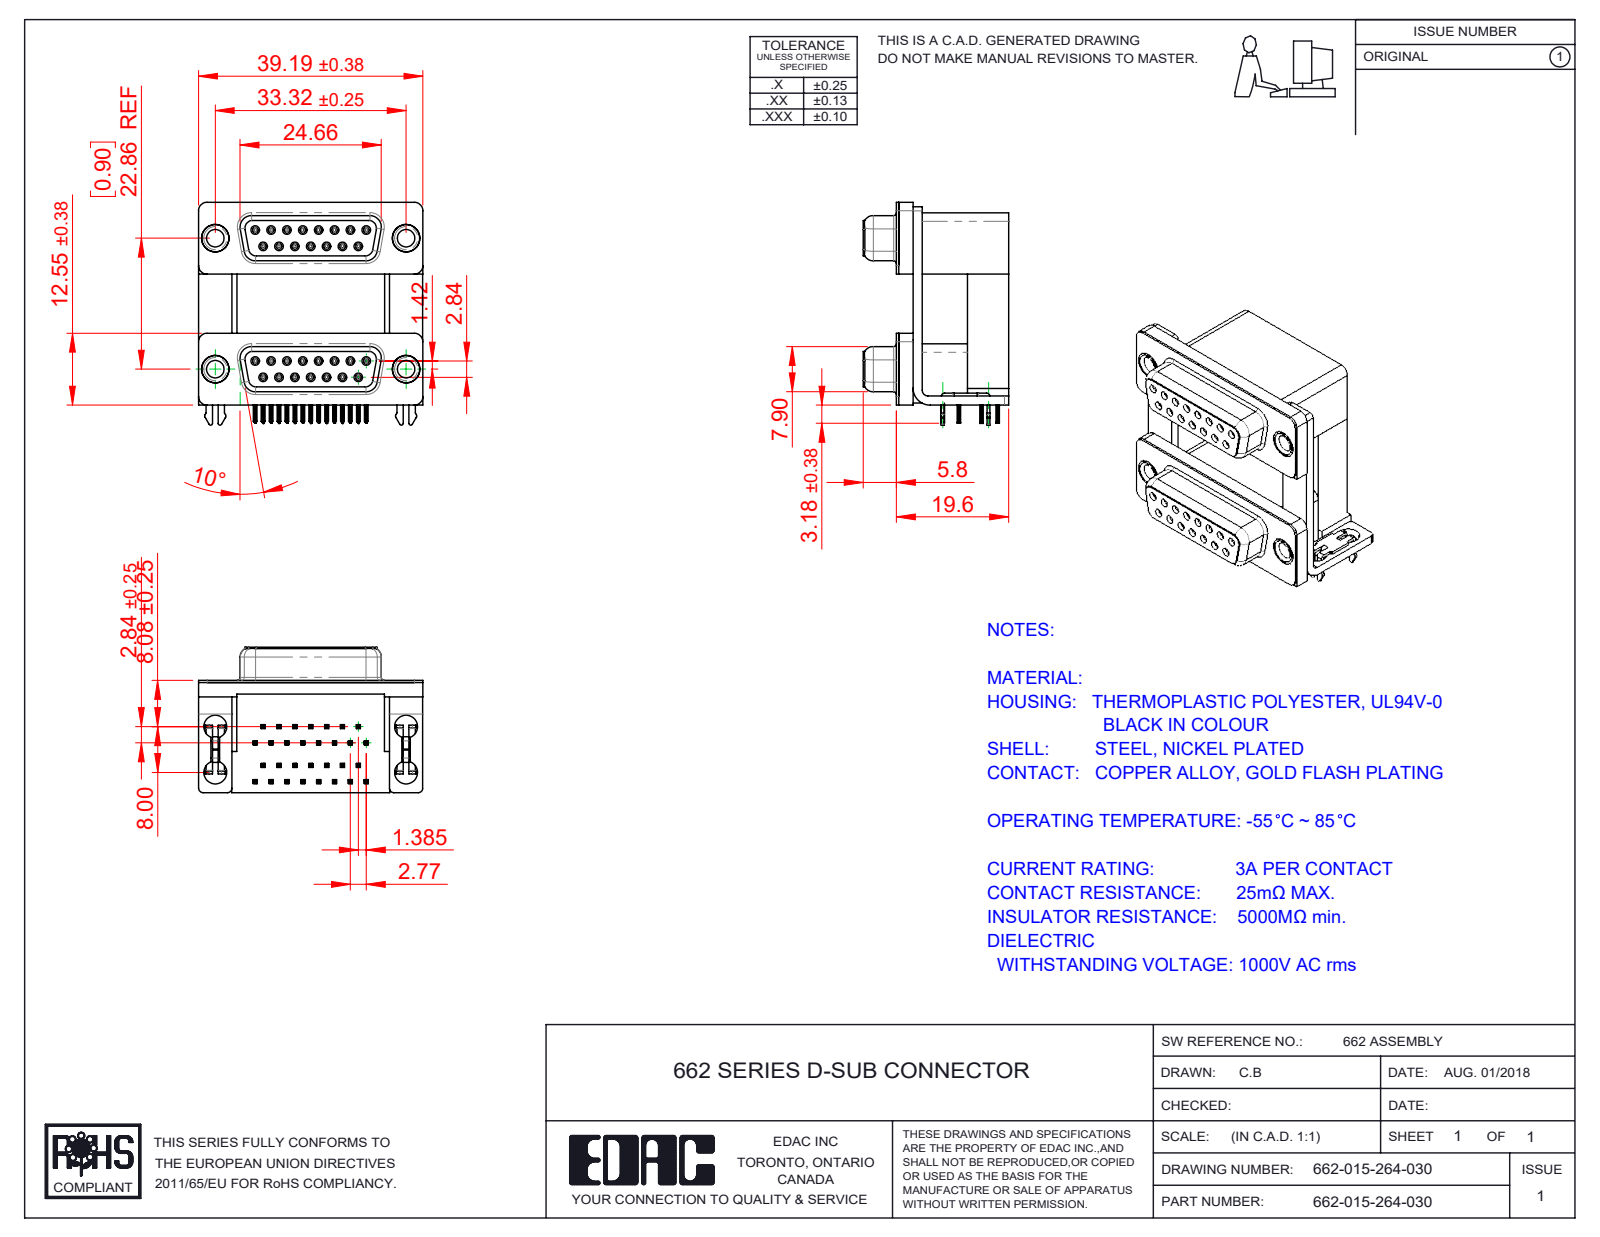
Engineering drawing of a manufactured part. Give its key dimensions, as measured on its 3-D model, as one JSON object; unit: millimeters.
{"part_name": "662 Contact Bottom Upper_H; 662 Contact Top Lower; 662 Thru Hole Rivet; 662 Mounting Bracket_2ProngH (+8 more)", "step_written_by": "SolidWorks 2020 (CONFIG_CONTROL_DESIGN)", "units": "millimeters", "bodies": {"solids": 43, "faces": 4930, "planar": 2298, "cylindrical": 1188, "other": 1444}, "overall_size": [39.19, 38.91, 25.4], "volume_mm3": 16761, "surface_area_mm2": 18839, "round_holes": [[0.8, 30], [0.9, 30], [4, 8], [3.05, 4], [3.5, 4], [4.8, 4], [5, 4]], "round_bosses_or_shafts": [[1.2, 30], [4.9, 4], [4.75, 4], [3.85, 4]], "partial_cylinders_radius": [[0.1, 242], [0.15, 120], [0.35, 60], [0.34, 30], [1.35, 16], [1.5, 16], [0.28, 14], [0.5, 12]], "face_to_face_distances": [19.2, 0.4, 22.86, 7.2, 12, 9.5, 16.7, 2.5, 2.9, 10.7], "hole_center_spacings": [3.16, 23.03, 2.77, 23.52, 5.54, 8.31, 22.86, 24.32]}
